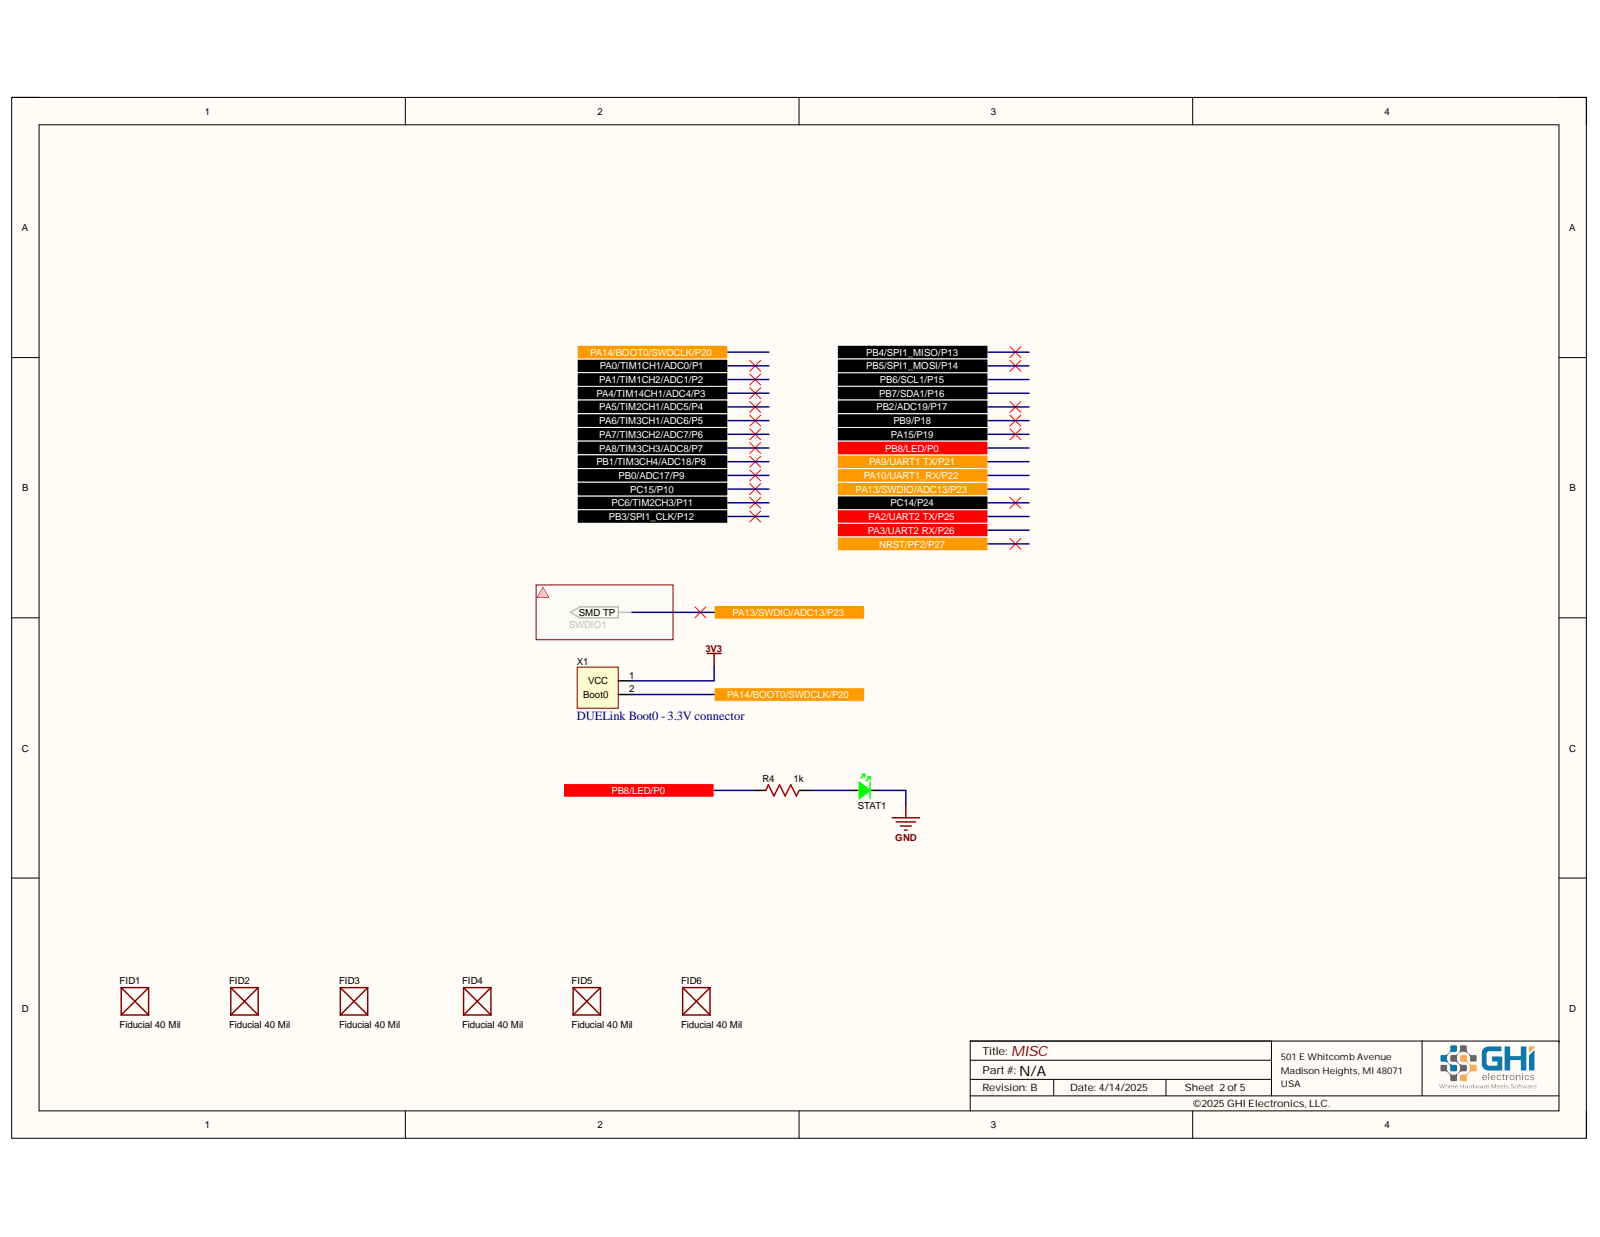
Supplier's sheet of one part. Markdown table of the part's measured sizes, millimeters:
| quantity | value |
| --- | --- |
| part name | PCB; Board; STAT1; 0603 LED Green (+5 more) |
| STEP written by | Open CASCADE 7.5 (AUTOMOTIVE_DESIGN) |
| units | millimeters |
| bodies | 88 solids, 1447 faces (1079 planar, 210 cylindrical, 158 other) |
| overall size | 20 × 17 × 7.52 |
| volume | 609 mm³ |
| surface area | 1 365 mm² |
| round holes (diameter × count) | 1.02 × 2, 3 × 2 |
| partial cylindrical surfaces (radius × count) | 0.12 × 35, 0.15 × 14, 0.17 × 2, 0.18 × 2, 0.18 × 2, 1.5 × 2, 3.5 × 2 |
| main face-to-face distances | 1.6, 0.55, 1, 1.85, 0.45, 2.53, 13.12, 16.45, 6, 5.5 |
| hole center spacings | 14.5, 2.54, 10, 16.87, 18.32 |
